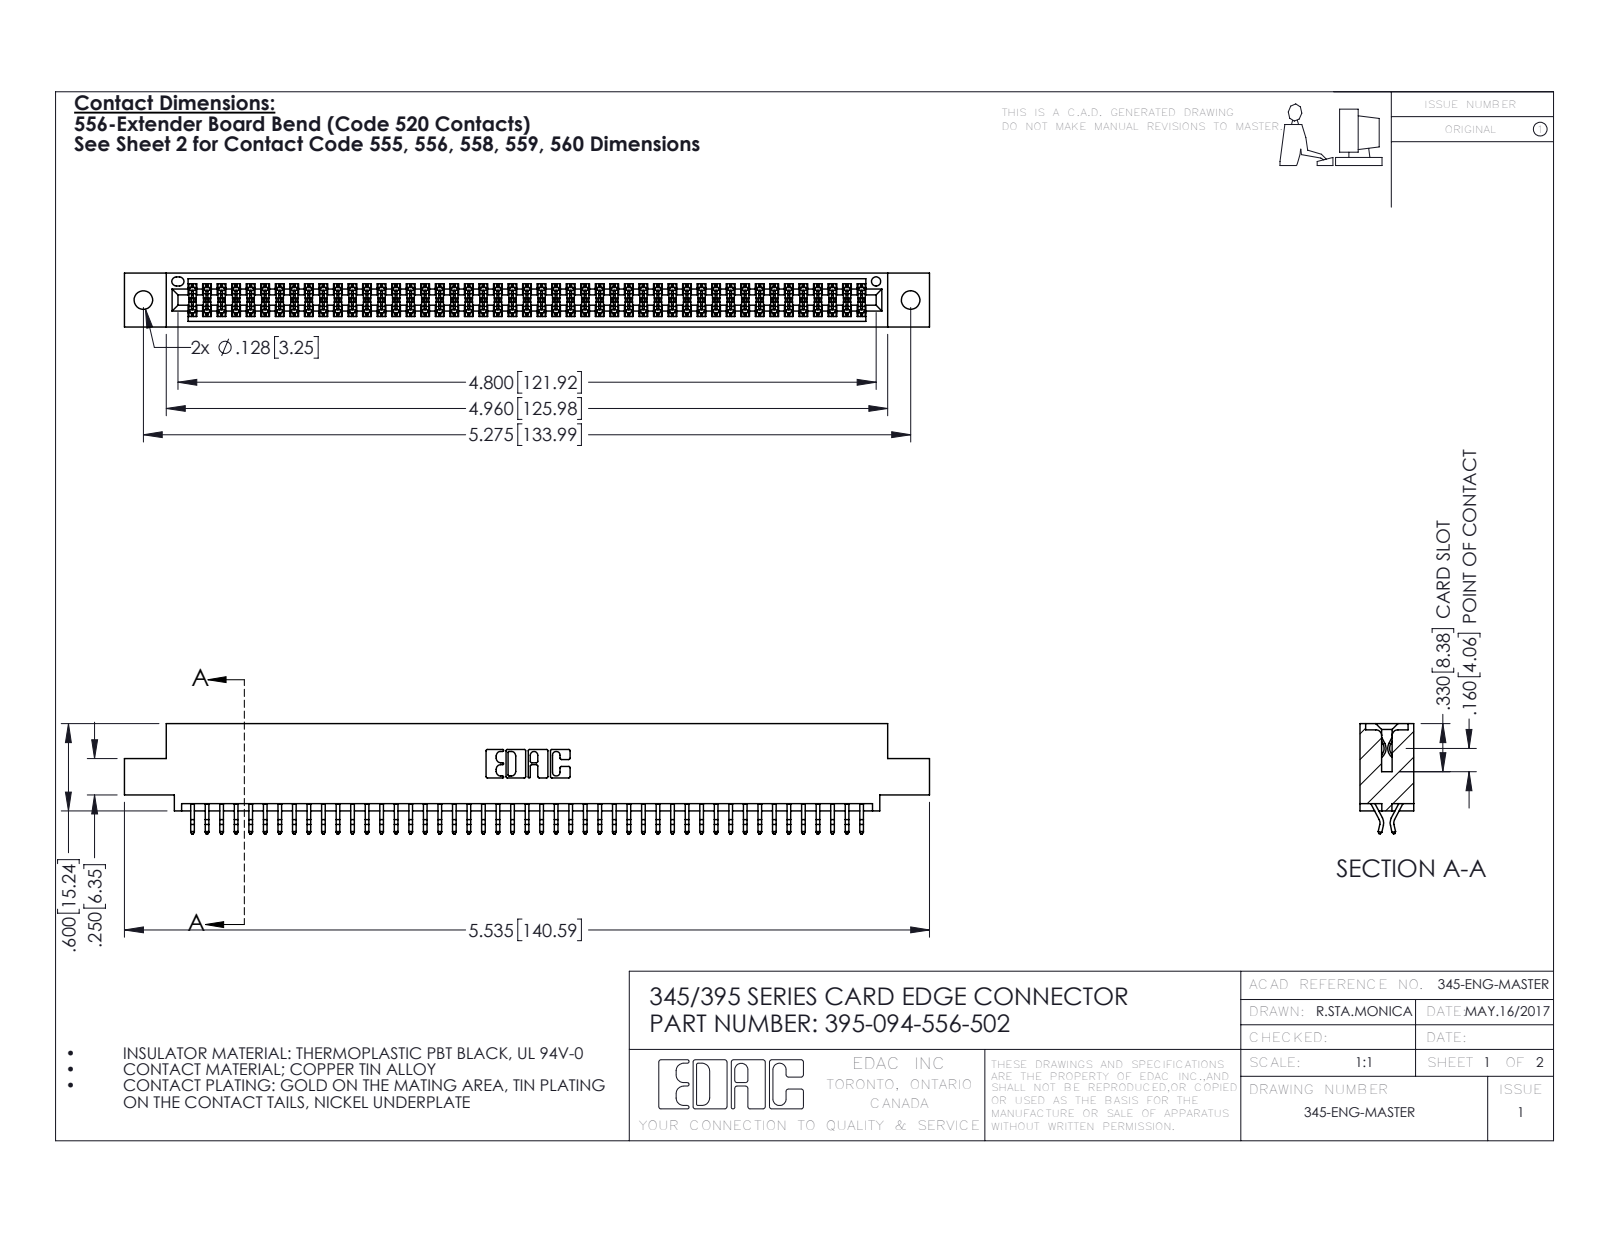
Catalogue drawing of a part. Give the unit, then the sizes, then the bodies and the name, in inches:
Units: inches
Overall size (bounding box): 5.535 × 0.757 × 0.37
Round holes (diameter × count): ⌀0.128 ×2, ⌀0.064 ×1
Partial cylindrical surfaces — rounded edges, fillets, slot ends (radius × count): R0.006 ×141, R0.01 ×22, R0.007 ×6, R0.031 ×6, R0.026 ×3, R0.01 ×2, R0.014 ×2, R0.019 ×2
Main face-to-face distances: 0.298, 0.072, 0.37, 0.2, 0.025, 0.098, 0.272, 0.225, 0.175, 0.149
Hole centre spacings: 0.27, 5.039, 5.275
Volume: 0.829 in³ · Surface area: 30.88 in²
Bodies: 95 solids, 5394 faces (3562 planar, 1832 cylindrical, 0 other)
Part name (STEP PRODUCT): 345 Part_0.110 Offset - 0.128 Dia; 395-094-556-502; 345-292-001_556 Tail
STEP written by: SolidWorks 2016 (CONFIG_CONTROL_DESIGN)
